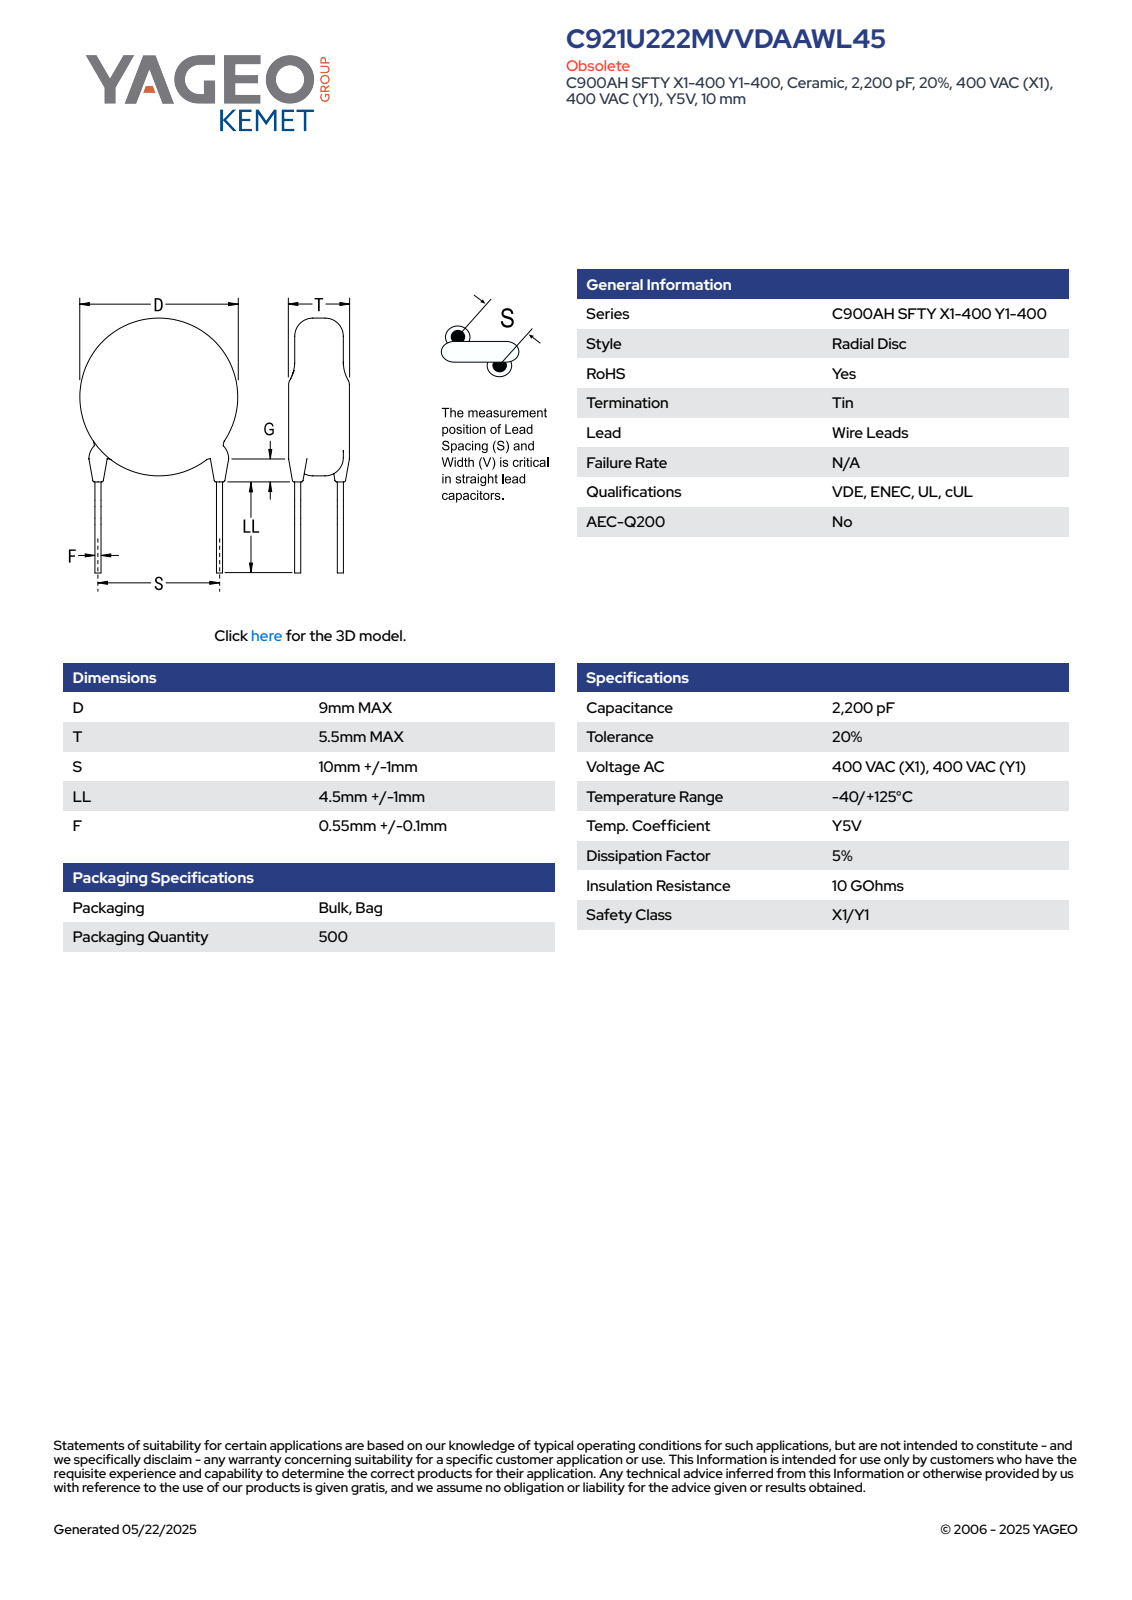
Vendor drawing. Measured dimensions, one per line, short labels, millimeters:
name: CCD_STC900_D9T5.5S10LL5.5F0.65G3
written by: SolidWorks 2014 (AUTOMOTIVE_DESIGN)
unit: mm
bodies: 4 solids, 83 faces (61 planar, 6 cylindrical, 16 other)
size: 14.88 × 10.15 × 5.5
volume: 346 mm³; area: 300 mm²
bosses: 2× ⌀0.65, 1× ⌀9
face distances: 5.5, 1.04, 10.9, 9.86, 0.84, 0.45, 0.39, 2.14, 3.08, 3.2
